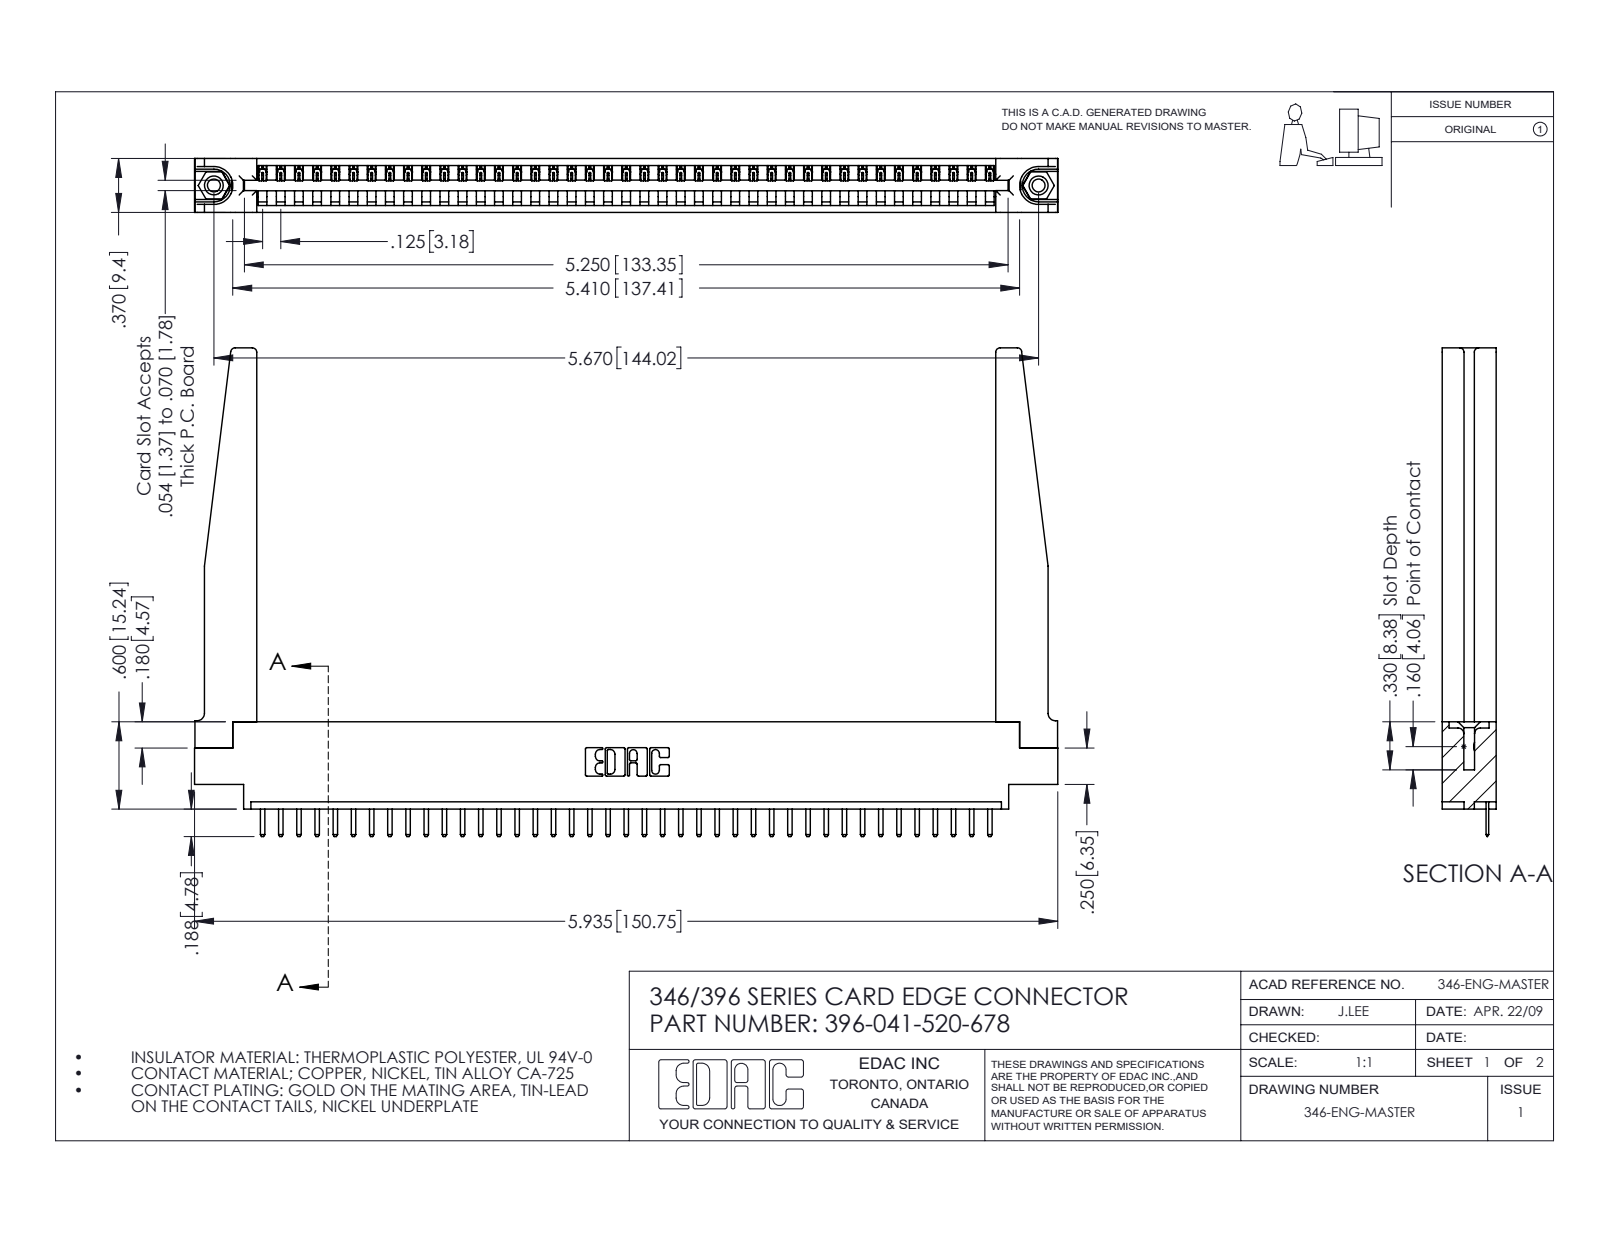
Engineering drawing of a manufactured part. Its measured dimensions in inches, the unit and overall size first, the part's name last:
Units: inches
Overall size (bounding box): 5.935 × 3.358 × 0.37
Round holes (diameter × count): ⌀0.089 ×2, ⌀0.125 ×2, ⌀0.156 ×2, ⌀0.064 ×1
Round bosses / shafts (diameter × count): ⌀0.155 ×2
Partial cylindrical surfaces — rounded edges, fillets, slot ends (radius × count): R0.01 ×84, R0.006 ×82, R0.01 ×22, R0.03 ×8, R0.007 ×6, R0.031 ×6, R0.026 ×3, R0.031 ×2
Main face-to-face distances: 0.37, 0.048, 0.322, 0.148, 0.072, 0.15, 0.25, 0.222, 0.1, 0.174
Hole centre spacings: 0.246, 5.461, 5.67
Volume: 1.285 in³ · Surface area: 37.17 in²
Bodies: 46 solids, 2902 faces (1944 planar, 906 cylindrical, 52 other)
Part name (STEP PRODUCT): 345-292-001_345-293-120; 346-220-078_345-220-078; 345-250-001_345-250-001-102; 346 Part_0.170 Offset - 0.156 Dia-TH (+1 more)
STEP written by: SolidWorks 2016 (CONFIG_CONTROL_DESIGN)
